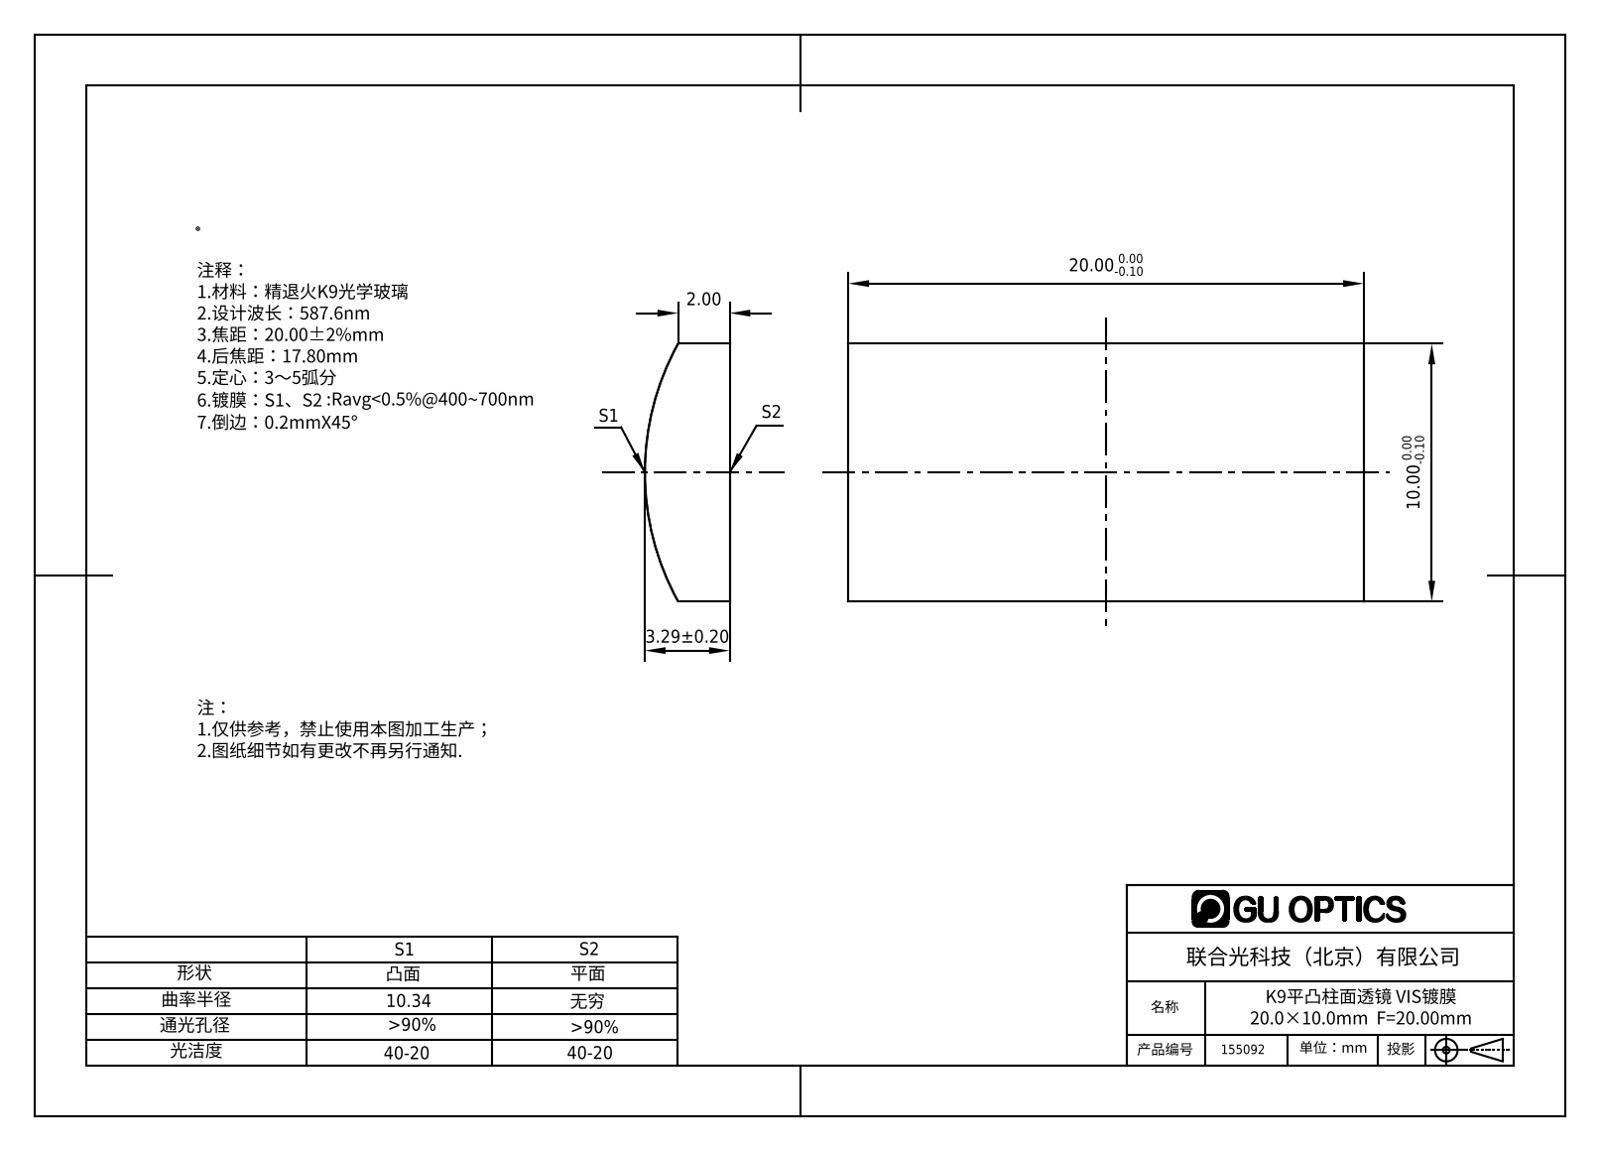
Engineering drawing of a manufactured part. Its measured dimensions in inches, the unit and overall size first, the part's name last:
Units: inches
Overall size (bounding box): 0.787 × 0.394 × 0.13
Partial cylindrical surfaces — rounded edges, fillets, slot ends (radius × count): R0.407 ×1
Main face-to-face distances: 0.394, 0.787
Volume: 0.035 in³ · Surface area: 0.846 in²
Bodies: 1 solid, 6 faces (5 planar, 1 cylindrical, 0 other)
Part name (STEP PRODUCT): 155026
STEP written by: SolidWorks 2016 (AUTOMOTIVE_DESIGN)
